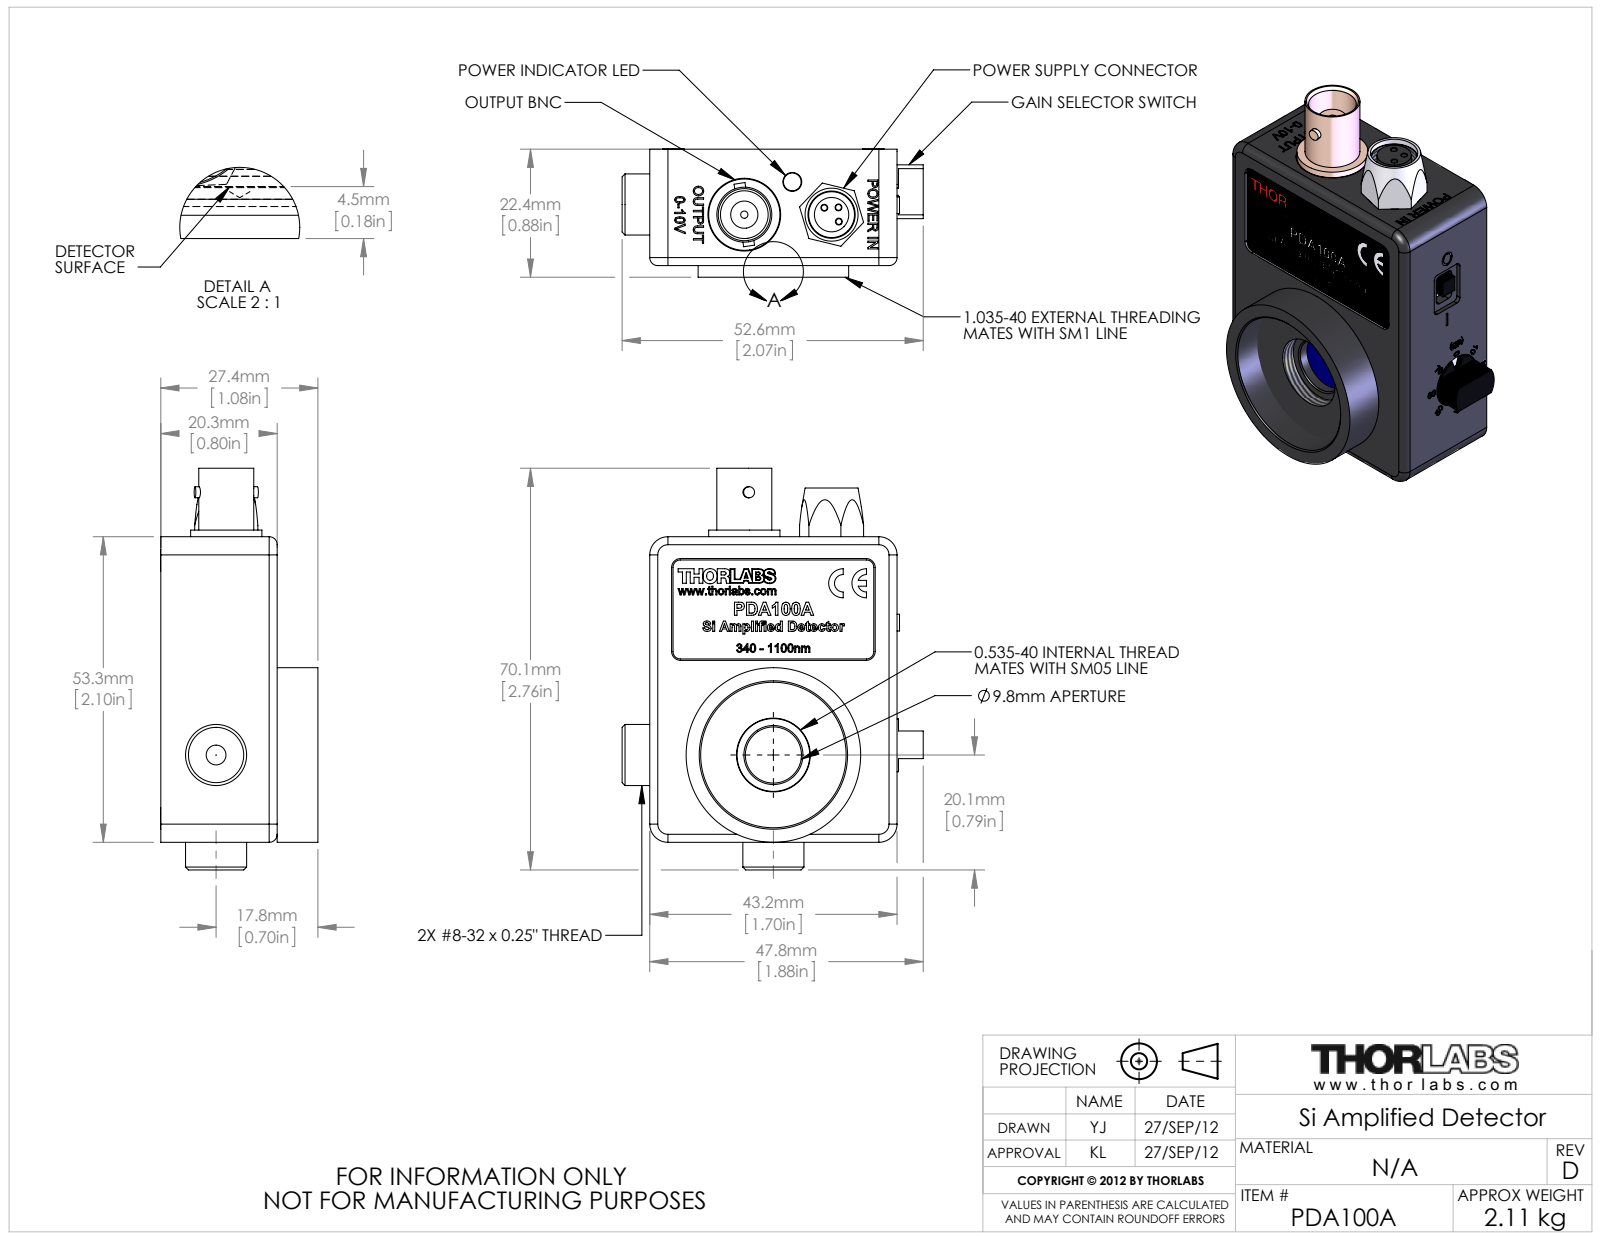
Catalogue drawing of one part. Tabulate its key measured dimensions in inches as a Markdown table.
| quantity | value |
| --- | --- |
| part name | 13055-E0W |
| STEP written by | SolidWorks 2011 (AUTOMOTIVE_DESIGN) |
| units | inches |
| bodies | 48 solids, 3428 faces (1676 planar, 837 cylindrical, 915 other) |
| overall size | 2.761 × 2.07 × 1.081 |
| volume | 1.554 in³ |
| surface area | 46.35 in² |
| round holes (diameter × count) | 0.037 × 9, 0.032 × 8, 0.07 × 7, 0.096 × 6, 0.125 × 4, 0.2 × 4, 0.039 × 3, 0.05 × 3, 0.025 × 2, 0.045 × 2, 0.136 × 2, 0.15 × 2 |
| round bosses / shafts (diameter × count) | 0.086 × 7, 0.147 × 4, 0.14 × 3, 0.063 × 3, 0.55 × 2, 0.42 × 2, 0.37 × 2, 0.236 × 2 |
| partial cylindrical surfaces (radius × count) | 0.008 × 36, 0.125 × 23, 0.004 × 16, 0.031 × 8, 0.095 × 8, 0.05 × 5, 0.055 × 4, 0.063 × 4 |
| main face-to-face distances | 0.063, 0.1, 0.502, 0.565, 0.062, 0.503, 0.05, 0.44, 0.02, 0.227 |
| hole center spacings | 0.1, 0.079, 0.126, 0.128, 0.141, 0.203, 0.28, 0.069 |
